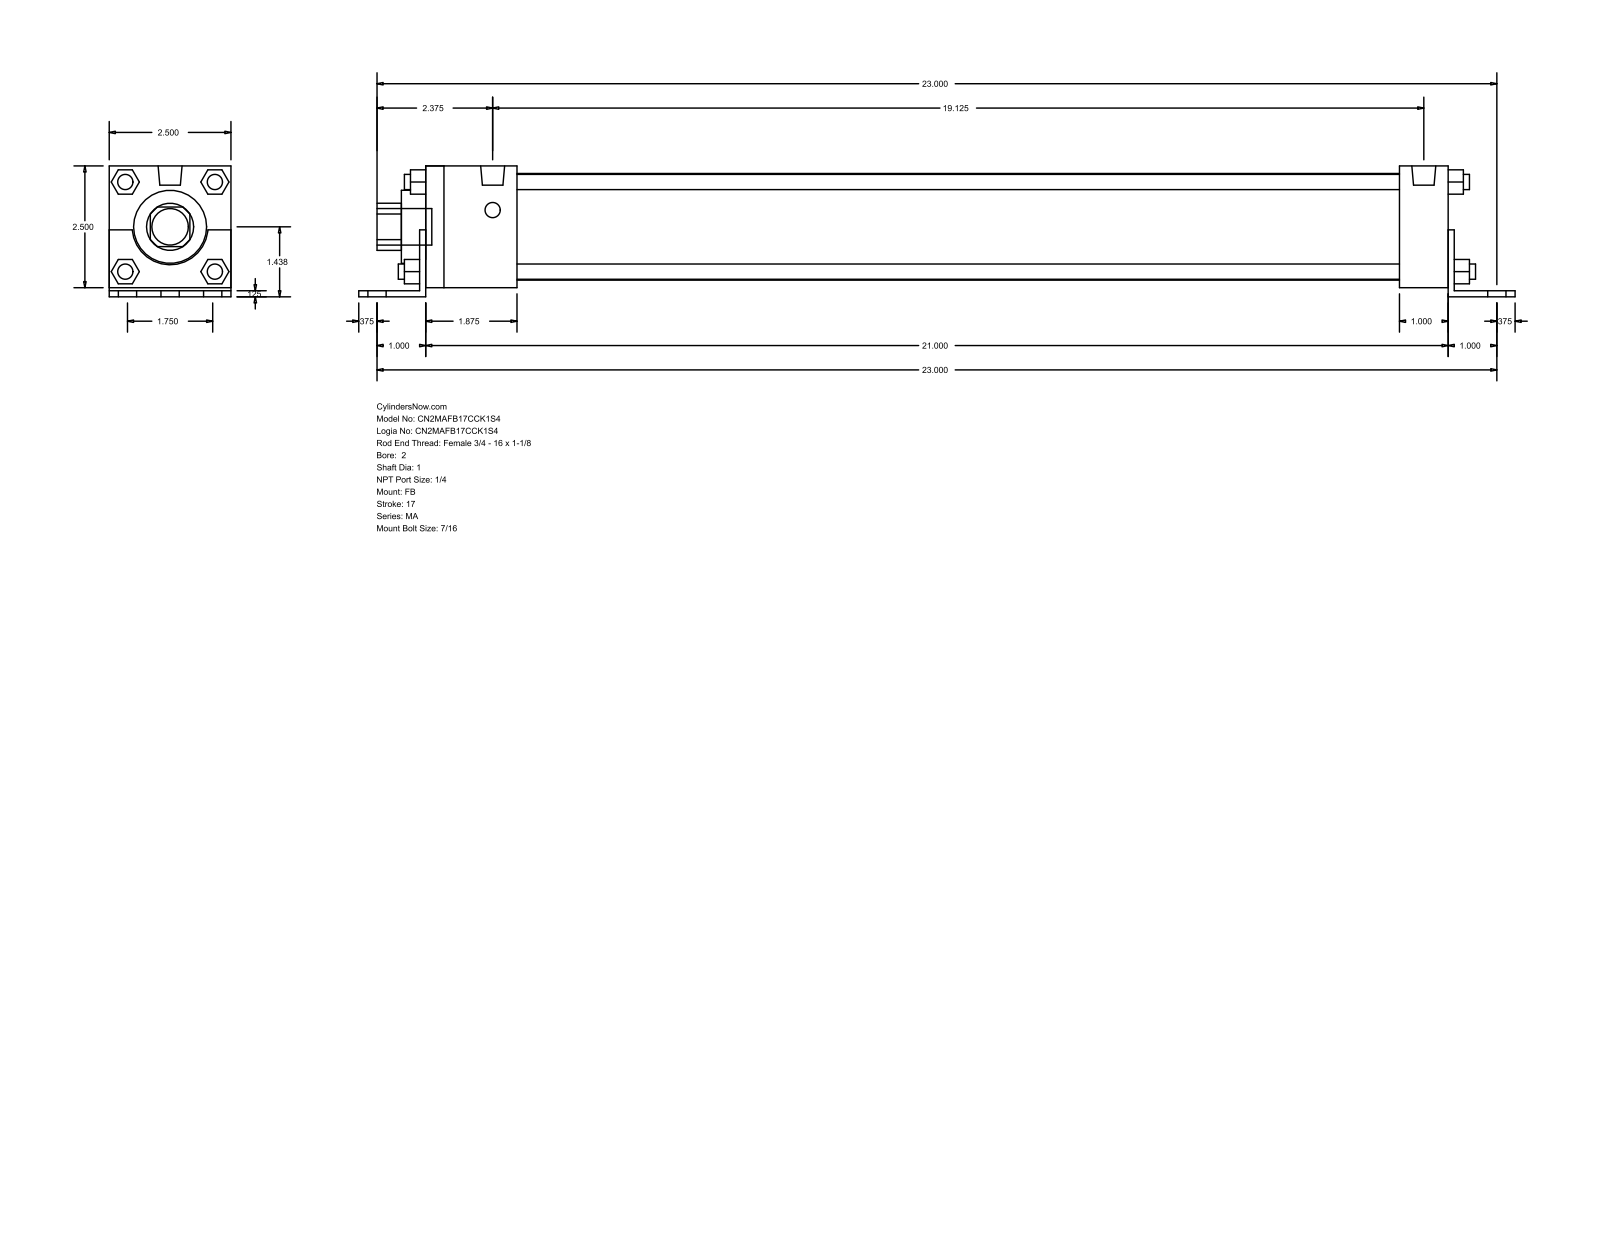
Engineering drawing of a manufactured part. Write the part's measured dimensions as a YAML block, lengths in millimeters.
part_name: "MA_FB__0200_1"
step_written_by: "GSSL Pune (CONFIG_CONTROL_DESIGN)"
units: millimeters
bodies: {solids: 0, faces: 140, planar: 105, cylindrical: 35, other: 0}
overall_size: [603.25, 68.26, 63.5]
round_holes:
  - {diameter: 25.4, count: 1}
  - {diameter: 38.1, count: 1}
  - {diameter: 55.63, count: 1}
round_bosses_or_shafts:
  - {diameter: 7.94, count: 8}
  - {diameter: 11.11, count: 6}
  - {diameter: 12.49, count: 2}
  - {diameter: 19.05, count: 1}
partial_cylinders:
  - {radius: 12.29, count: 1}
  - {radius: 19.81, count: 1}
face_to_face_distances: [63.5, 3.17, 4.76, 68.26, 1.59, 65.09, 12.7, 3.18, 533.4, 536.58]
